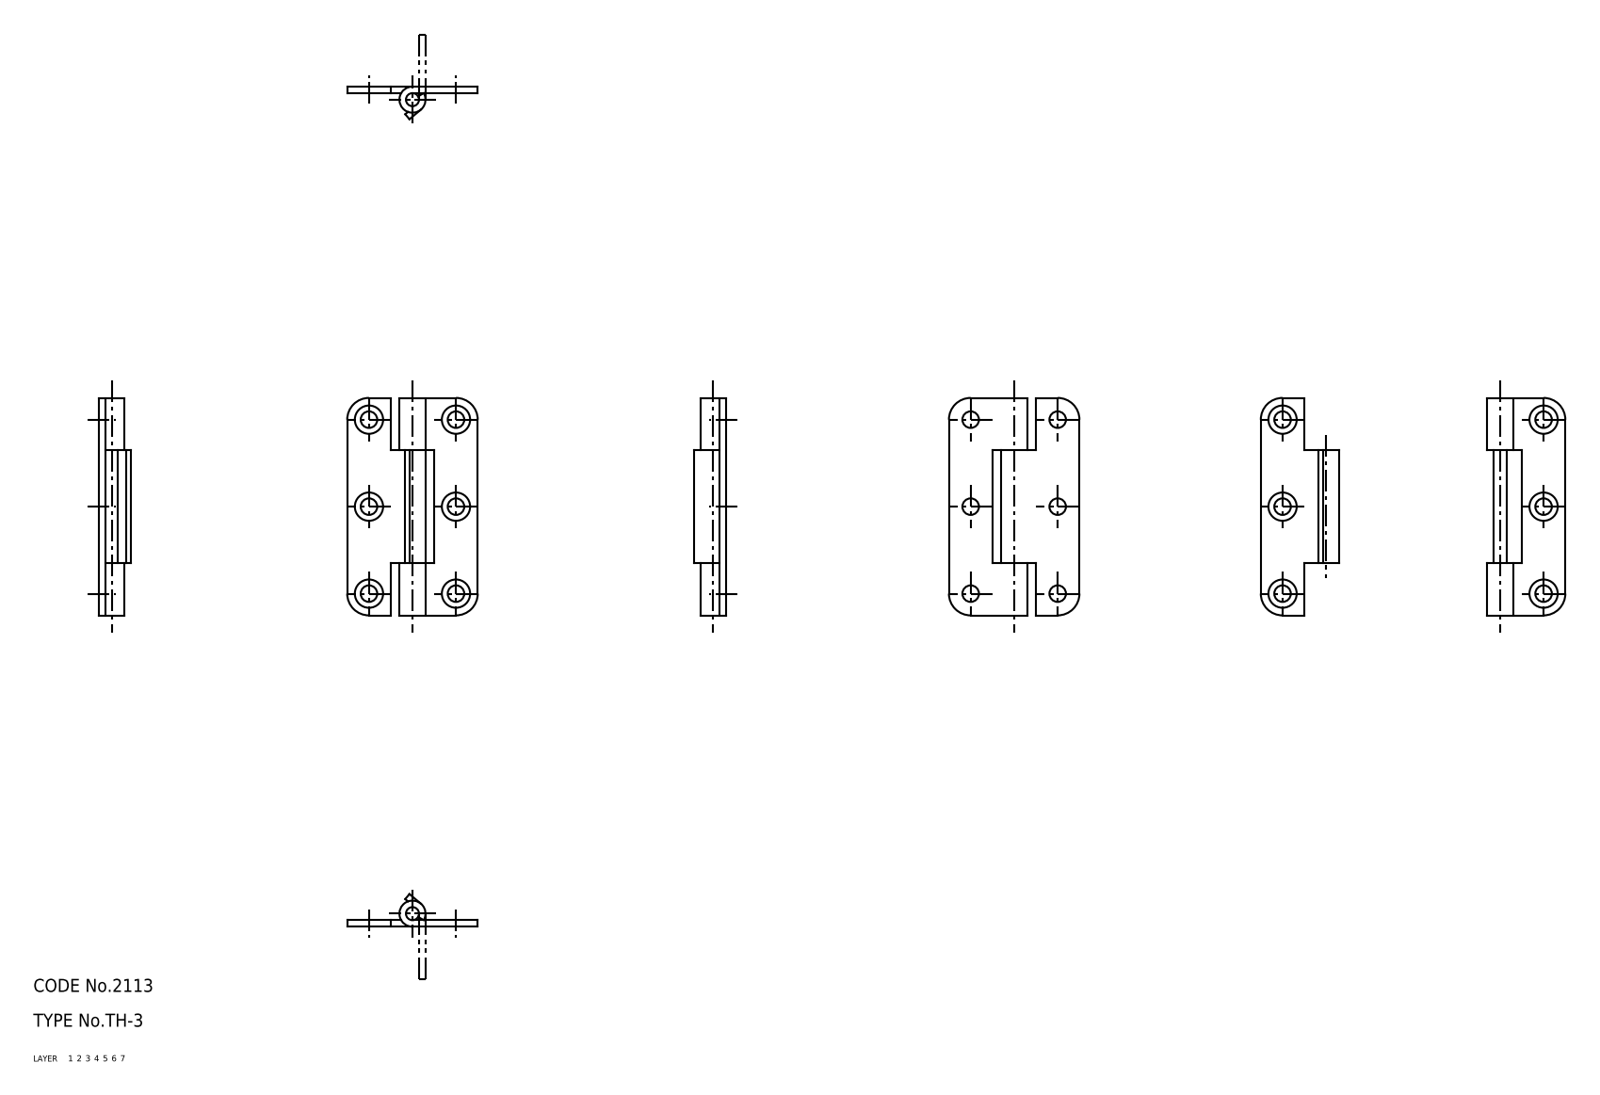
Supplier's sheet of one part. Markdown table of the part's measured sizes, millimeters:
| quantity | value |
| --- | --- |
| part name | shaft; hinge piece_B; hinge piece_A; TH_3_7579_36 |
| STEP written by | CADfix (AUTOMOTIVE_DESIGN) |
| units | millimeters |
| bodies | 3 solids, 60 faces (0 planar, 0 cylindrical, 60 other) |
| overall size | 50 × 30 × 7.5 |
| volume | 2 785 mm³ |
| surface area | 4 394 mm² |
